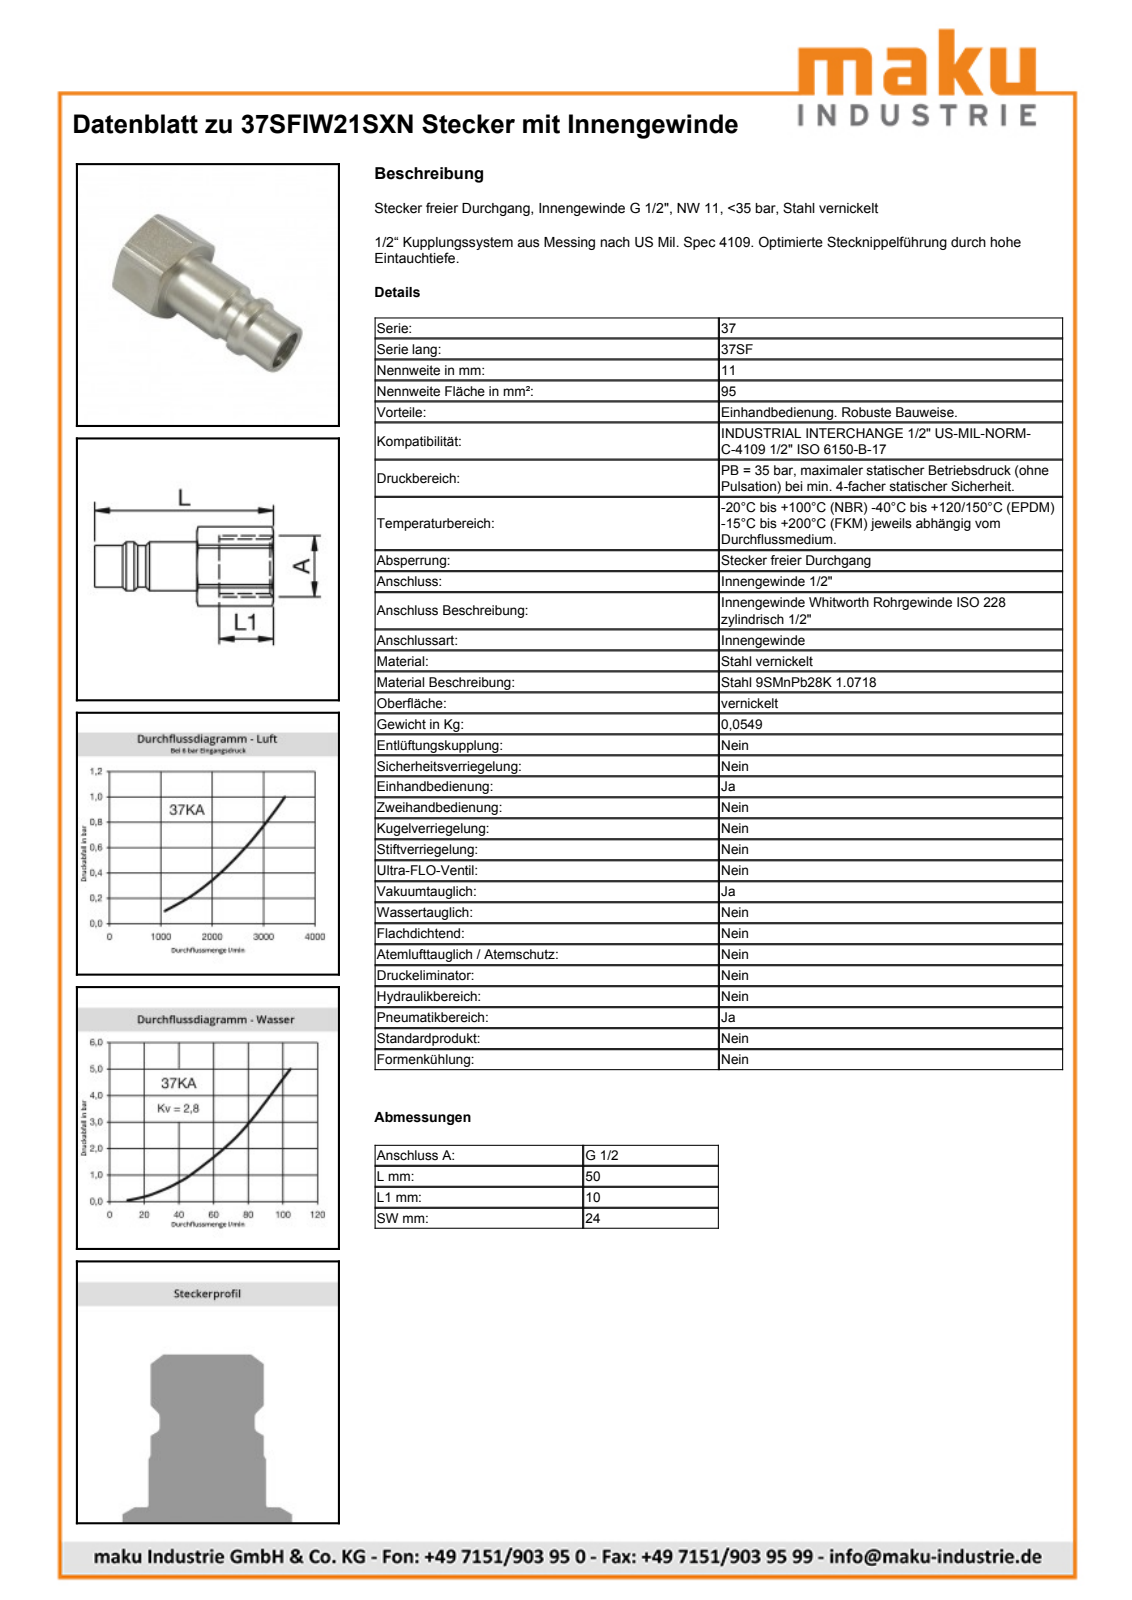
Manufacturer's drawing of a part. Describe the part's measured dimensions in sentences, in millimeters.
The part is named "D108363". Its 3-D file was written by "Autodesk Inventor 2013 (AUTOMOTIVE_DESIGN)". It is 1 solid with 39 faces: 10 planar, 12 cylindrical and 17 other. Overall it measures 50 by 27.05 by 24 millimeters. Its volume is 7 537 cubic millimeters and its surface area 5 698 square millimeters. Round holes: 1 of diameter 10.7, 1 of diameter 18.63. Round bosses or shafts: 1 of diameter 16.65, 1 of diameter 14.25, 1 of diameter 14.2. Partial cylindrical surfaces (rounded edges, fillets, slot ends): 1 of radius 13.53. The main face-to-face distances are 24, 3.1, 15.1, 12, 34.9, 38, 50.
